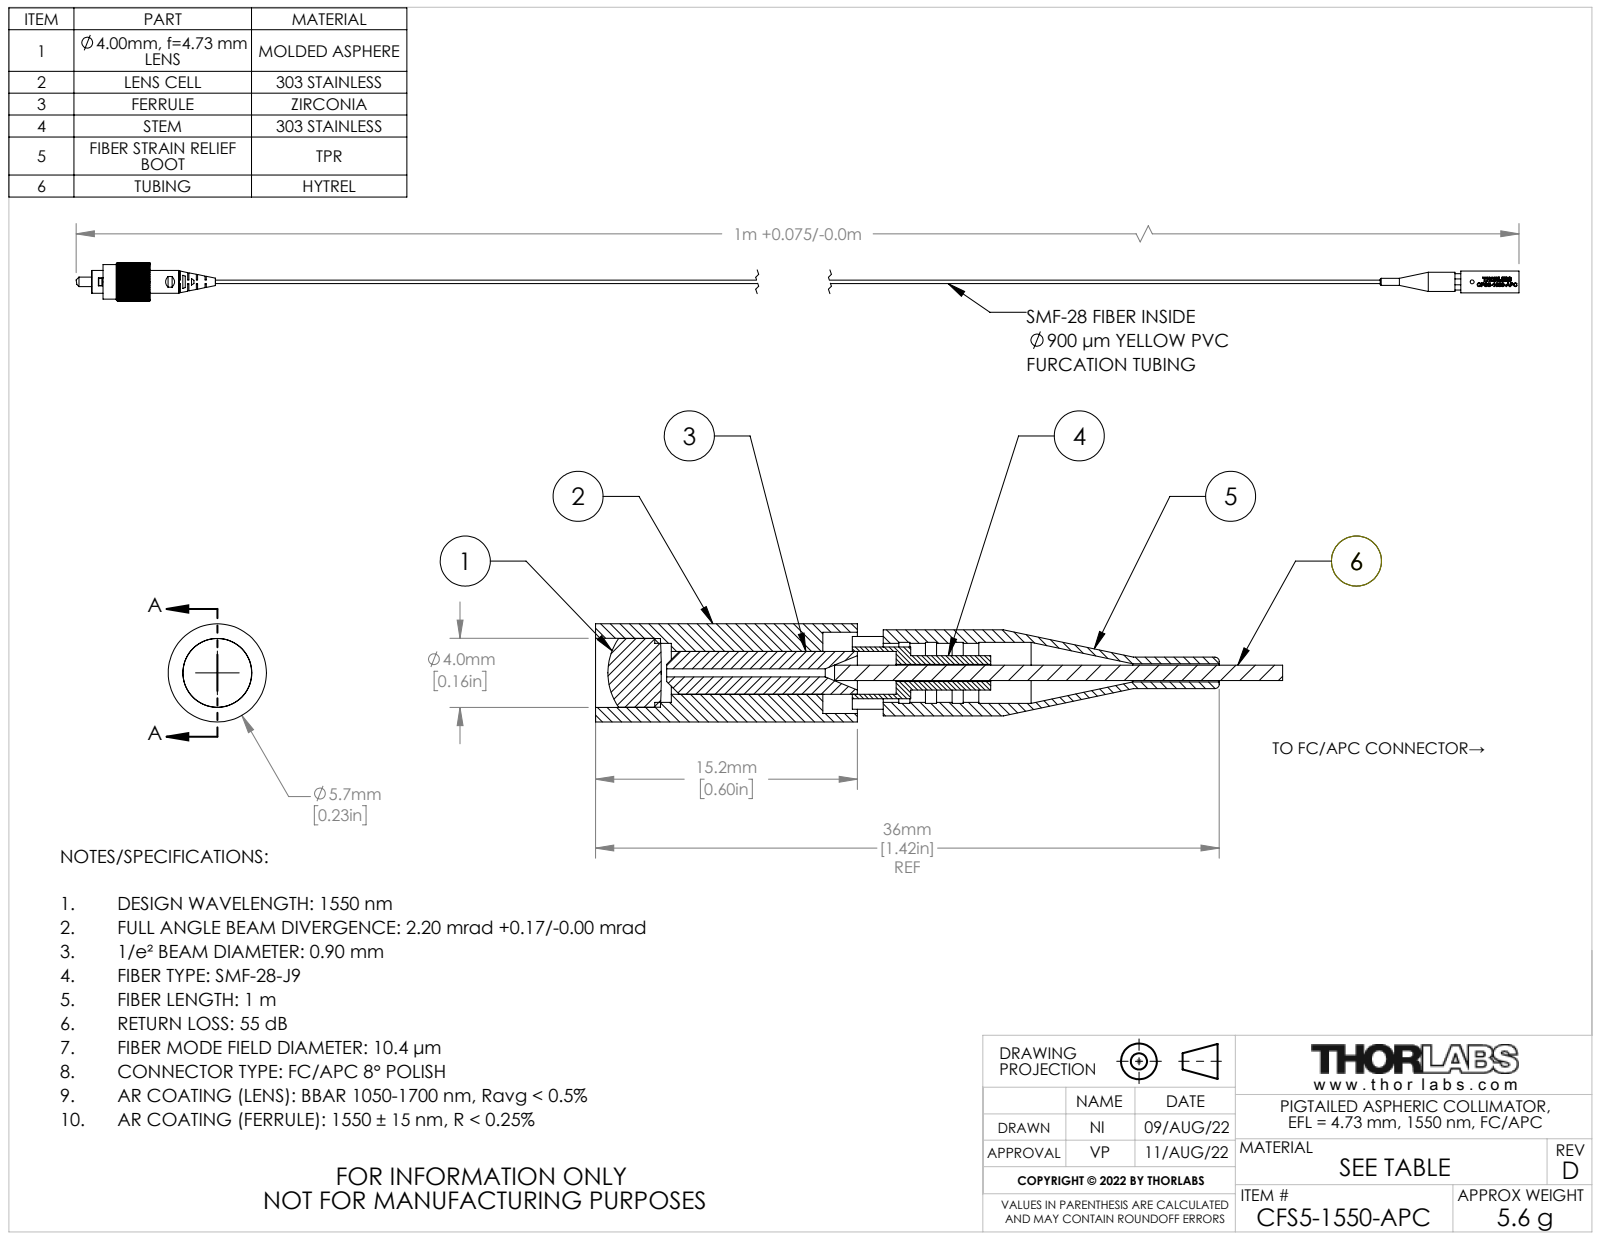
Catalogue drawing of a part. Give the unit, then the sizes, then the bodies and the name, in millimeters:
Units: millimetres
Overall size (bounding box): 1025.28 × 9.99 × 9.99
Round holes (diameter × count): ⌀1.02 ×3, ⌀0.46 ×1, ⌀1 ×1, ⌀1.07 ×1, ⌀1.4 ×1, ⌀2.5 ×1, ⌀2.5 ×1, ⌀3.01 ×1, ⌀3.05 ×1, ⌀3.43 ×1, ⌀3.43 ×1, ⌀3.55 ×1
Round bosses / shafts (diameter × count): ⌀7.11 ×1, ⌀5.97 ×1, ⌀5.71 ×1, ⌀5 ×1, ⌀4.95 ×1, ⌀4 ×1, ⌀3.81 ×1, ⌀3.56 ×1
Partial cylindrical surfaces — rounded edges, fillets, slot ends (radius × count): R2.25 ×1, R2.98 ×1, R5 ×1
Main face-to-face distances: 6.78, 1.57, 1.02, 2.59, 2.26, 0.31, 4.52, 15.24, 995.74, 2.01
Volume: 1 896 mm³ · Surface area: 6 196 mm²
Bodies: 9 solids, 495 faces (241 planar, 212 cylindrical, 42 other)
Part name (STEP PRODUCT): 17382-E0W
STEP written by: SolidWorks 2018 (CONFIG_CONTROL_DESIGN)
